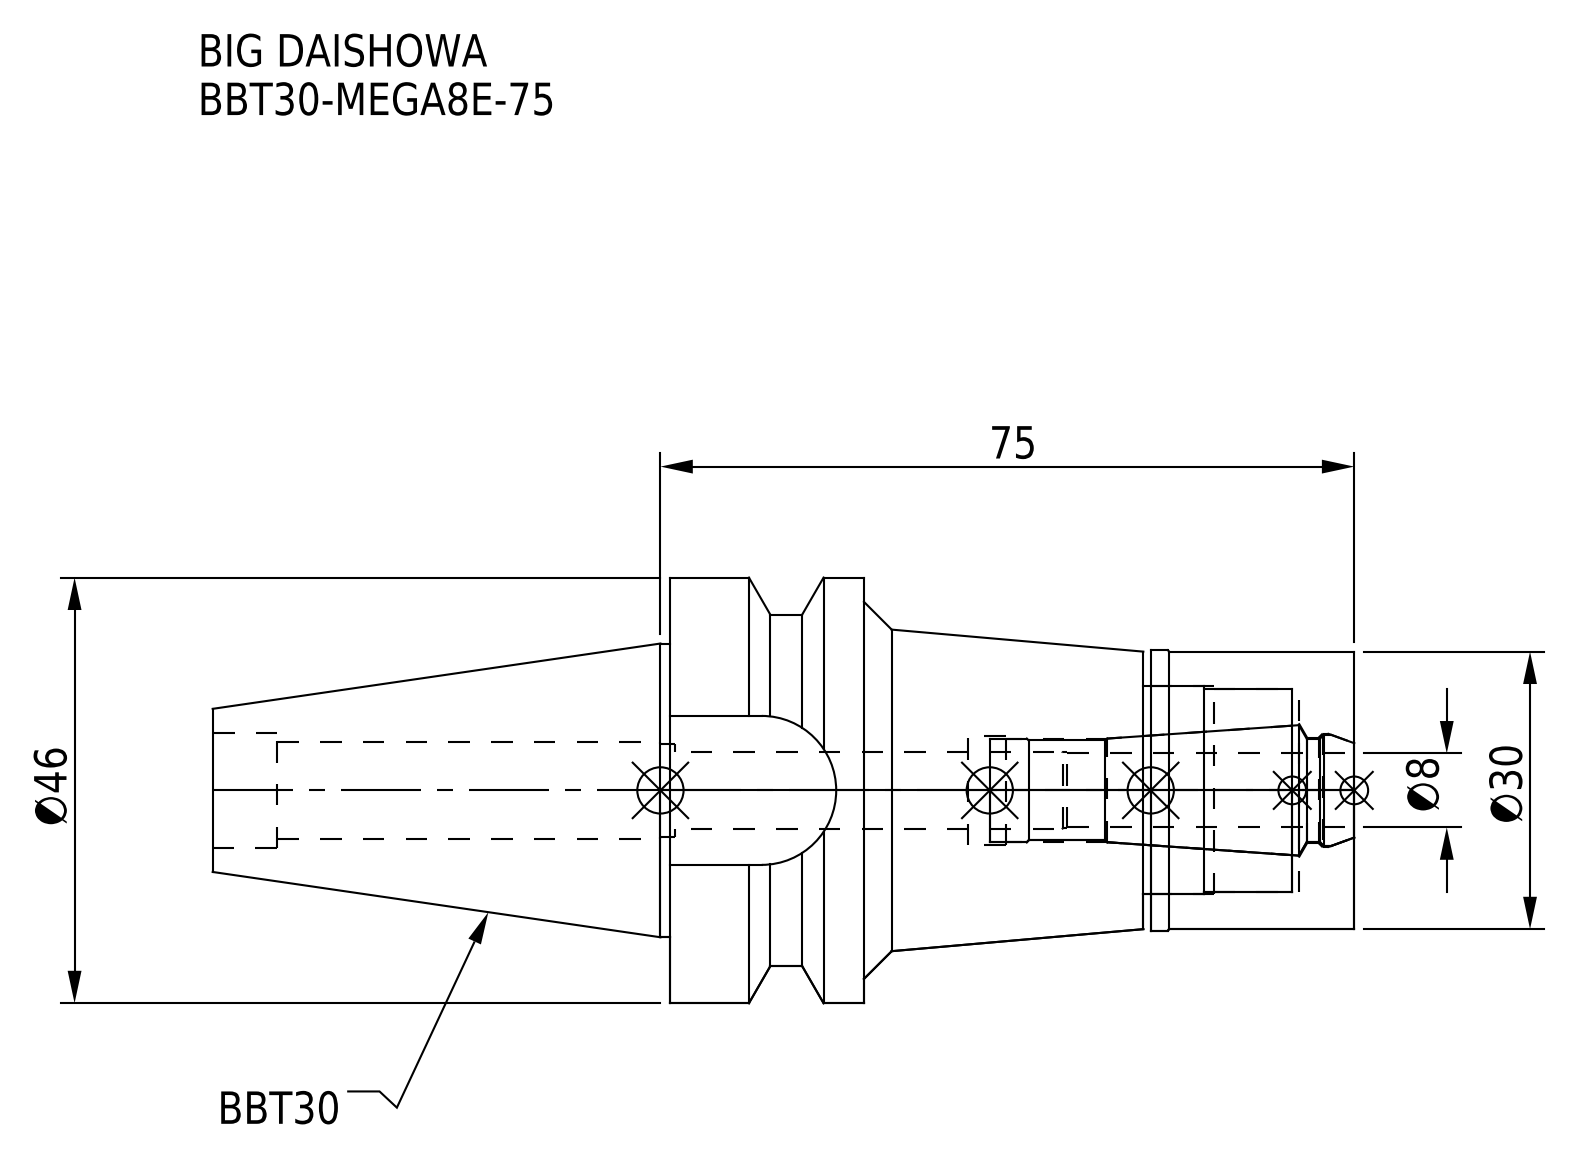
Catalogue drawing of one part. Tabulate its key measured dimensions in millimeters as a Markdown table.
| quantity | value |
| --- | --- |
| part name | BBT30ME08075-080_ASM.stp; BBT30-MEGA8E-75_1.stp; BBT30-MEGA8E-75-080-FreeParts; MEN8_1.stp (+3 more) |
| STEP written by | SolidWorks 2019 (CONFIG_CONTROL_DESIGN) |
| units | millimeters |
| bodies | 2 solids, 79 faces (21 planar, 38 cylindrical, 20 other) |
| overall size | 123.4 × 46 × 46 |
| volume | 84 318 mm³ |
| surface area | 22 383 mm² |
| round holes (diameter × count) | 8.4 × 1, 10 × 1, 10.4 × 1, 11.2 × 1, 11.4 × 1, 11.8 × 1, 12.3 × 1, 12.5 × 1, 22 × 1, 22.5 × 1 |
| round bosses / shafts (diameter × count) | 46 × 1, 31.75 × 1, 30.3 × 1, 30 × 1 |
| partial cylindrical surfaces (radius × count) | 8.05 × 1, 19 × 1 |
| main face-to-face distances | 74, 53, 21, 31, 22, 16.1, 52, 22.8, 0.8, 30.2 |
